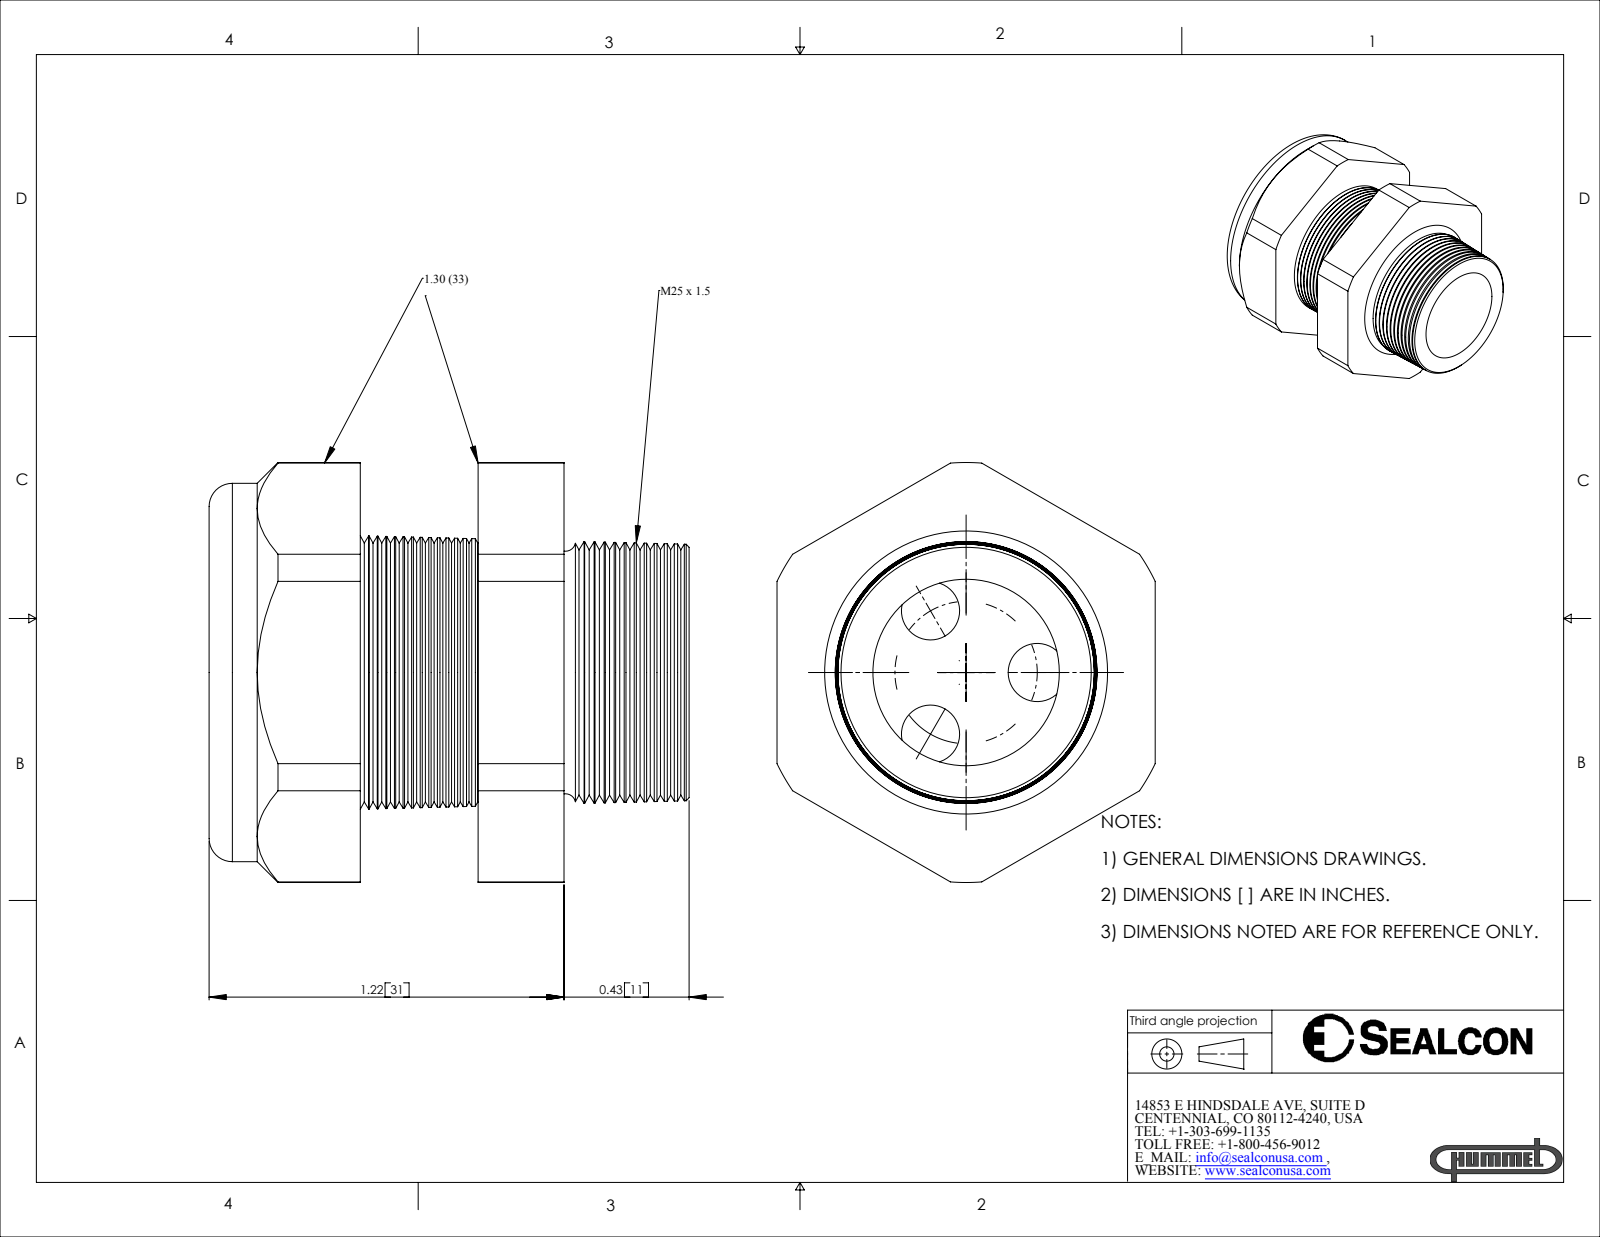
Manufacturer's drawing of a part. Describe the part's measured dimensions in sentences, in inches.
The part is named "CD25M7-GY". Its 3-D file was written by "SolidWorks 2007 (CONFIG_CONTROL_DESIGN)". It is 2 solids with 212 faces: 20 planar, 26 cylindrical and 166 other. Overall it measures 1.65 by 1.443 by 1.3 inches. Its volume is 1.16 cubic inches and its surface area 16.99 square inches. Round holes: 3 of diameter 0.2, 1 of diameter 0.69, 1 of diameter 0.71. Round bosses or shafts: 1 of diameter 1.3. Partial cylindrical surfaces (rounded edges, fillets, slot ends): 1 of radius 0.721. The main face-to-face distances are 1.3, 0.405, 0.7, 0.295, 0.52, 0.925, 1.22, 0.35, 0.17, 0.575. The hole center spacings are 0.244, 0.424.
